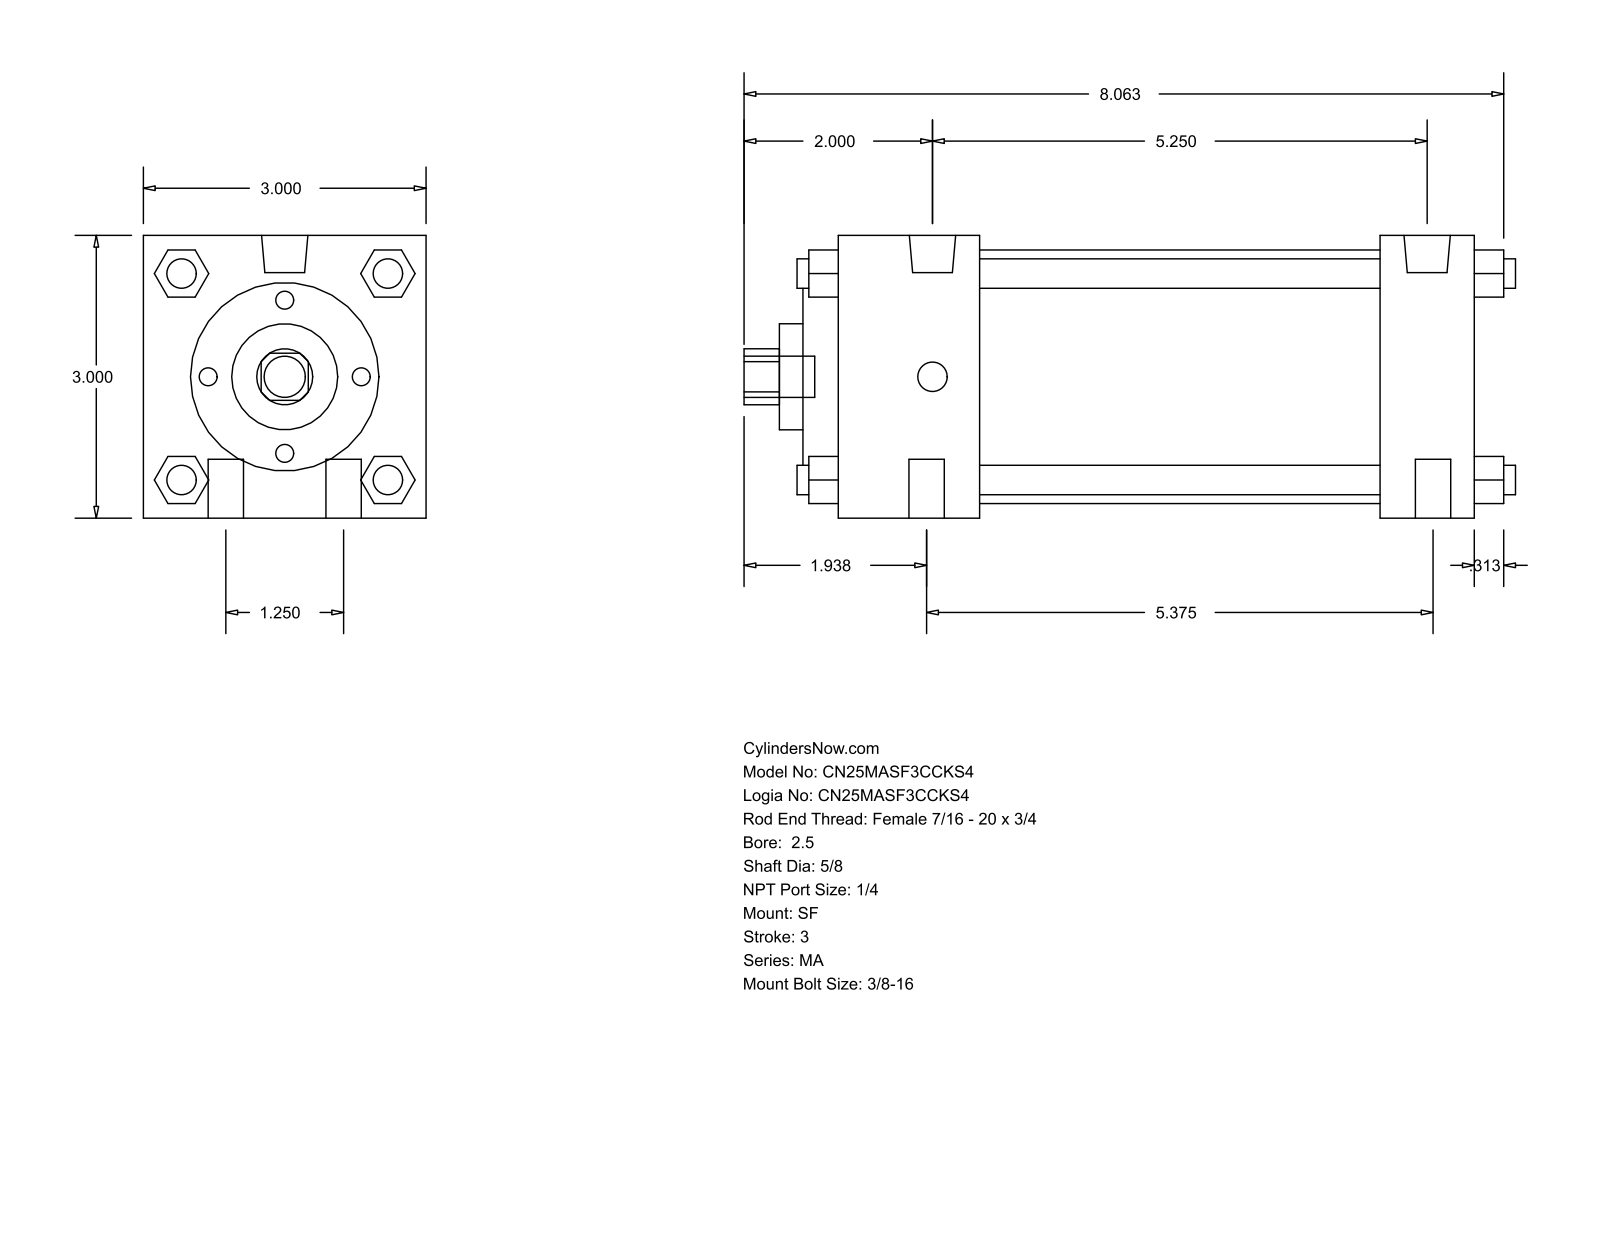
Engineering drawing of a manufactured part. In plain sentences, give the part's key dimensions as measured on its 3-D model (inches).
The part is named "MA_SF__0250_0.625". Its 3-D file was written by "GSSL Pune (CONFIG_CONTROL_DESIGN)". It is 0 solids with 126 faces: 95 planar, 31 cylindrical and 0 other. Overall it measures 8.187 by 3 by 3 inches. Round holes: 1 of diameter 0.625, 1 of diameter 1.125, 1 of diameter 2, 1 of diameter 2.69. Round bosses or shafts: 6 of diameter 0.313, 4 of diameter 0.375, 2 of diameter 0.492, 1 of diameter 0.437. Partial cylindrical surfaces (rounded edges, fillets, slot ends): 1 of radius 0.297. The main face-to-face distances are 3, 6.75, 1, 5.75, 1.5, 4.25, 5.25, 0.5, 0.375, 1.875.
